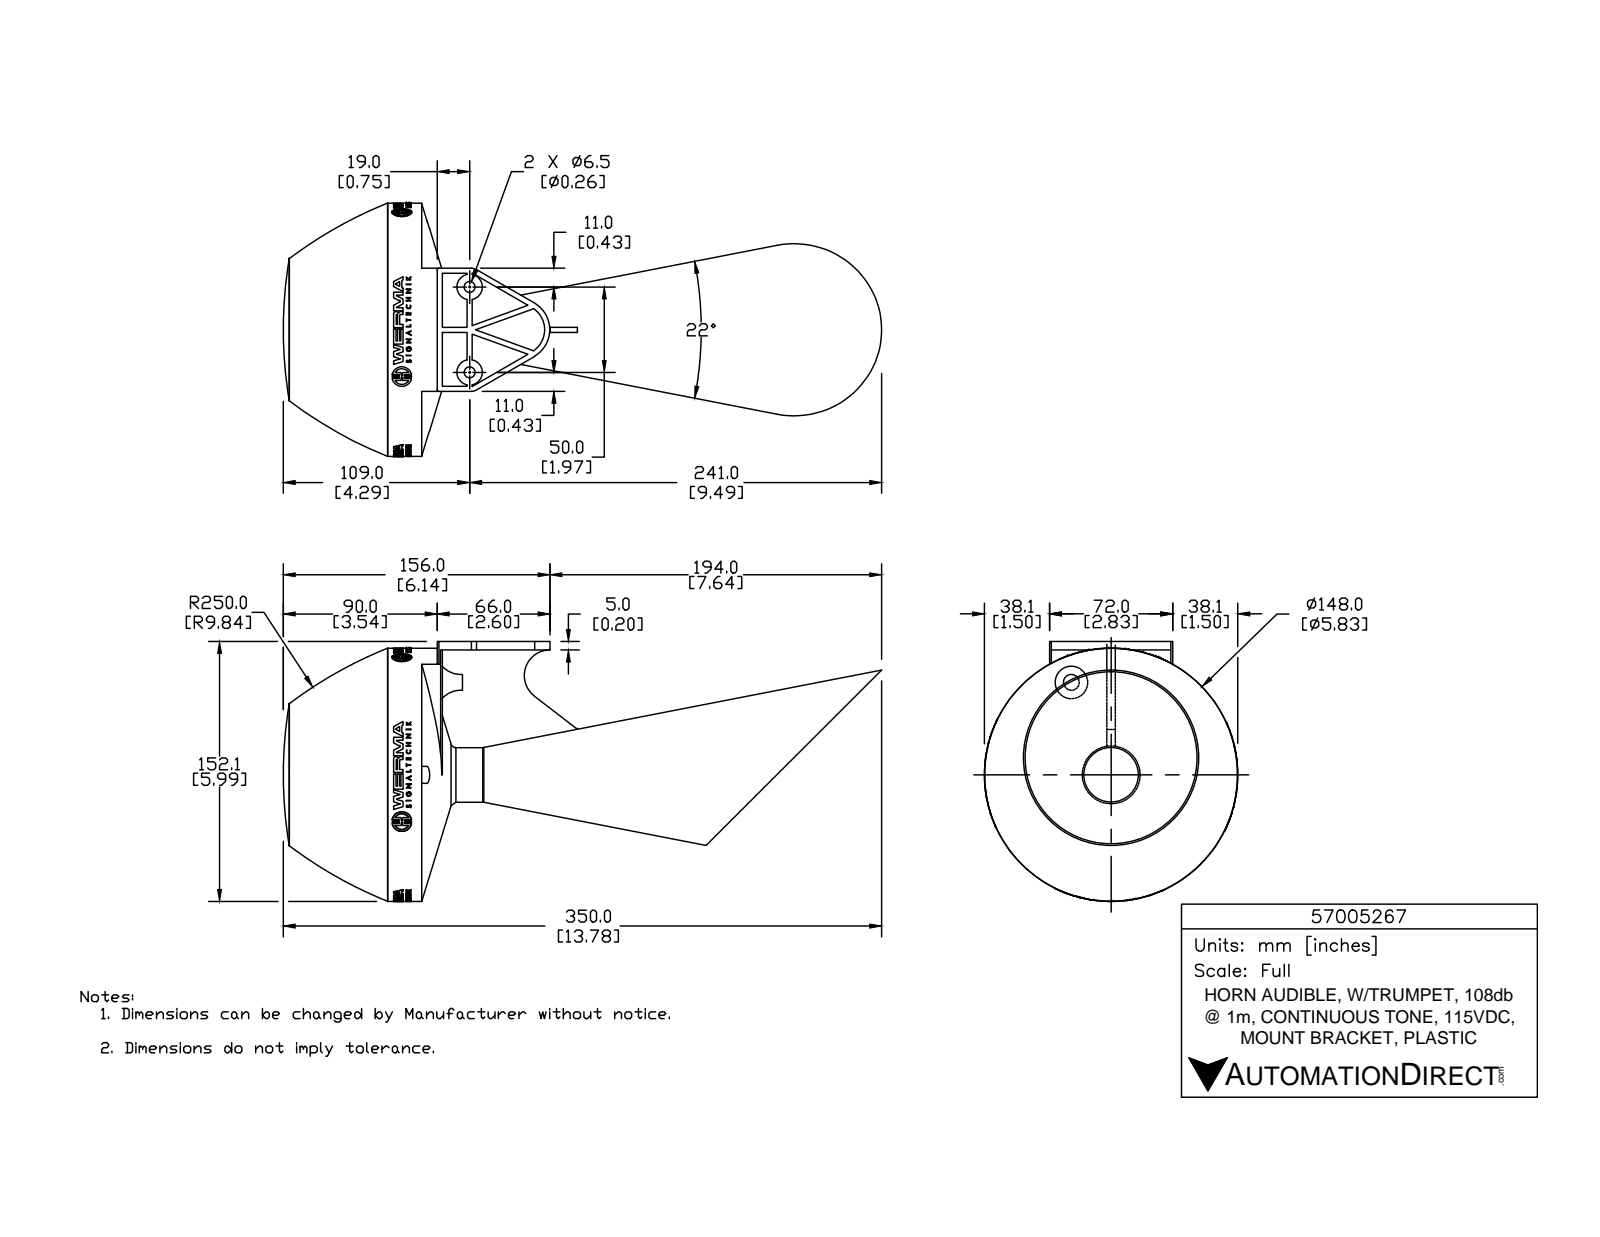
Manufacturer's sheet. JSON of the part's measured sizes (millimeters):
{"part_name": "57005267", "step_written_by": "SolidWorks 2017 (AUTOMOTIVE_DESIGN)", "units": "millimeters", "bodies": {"solids": 10, "faces": 1177, "planar": 759, "cylindrical": 381, "other": 37}, "overall_size": [350, 152.1, 148.2], "volume_mm3": 1308000, "surface_area_mm2": 156700, "round_holes": [[2, 4], [6.5, 2], [16, 1], [23, 1], [118, 1]], "round_bosses_or_shafts": [[11.5, 4], [2.9, 4], [15, 2], [148, 1], [32, 1], [26, 1], [19, 1]], "partial_cylinders_radius": [[0.2, 12], [0.2, 8], [0.4, 8], [0.4, 8], [0.4, 8], [6.7, 8], [0.2, 4], [0.2, 4]], "face_to_face_distances": [3, 12, 5, 2, 9, 34.5, 37.5, 24.3, 27.3, 36.3], "hole_center_spacings": [22.4, 38.2, 50.8, 50, 56.1]}
